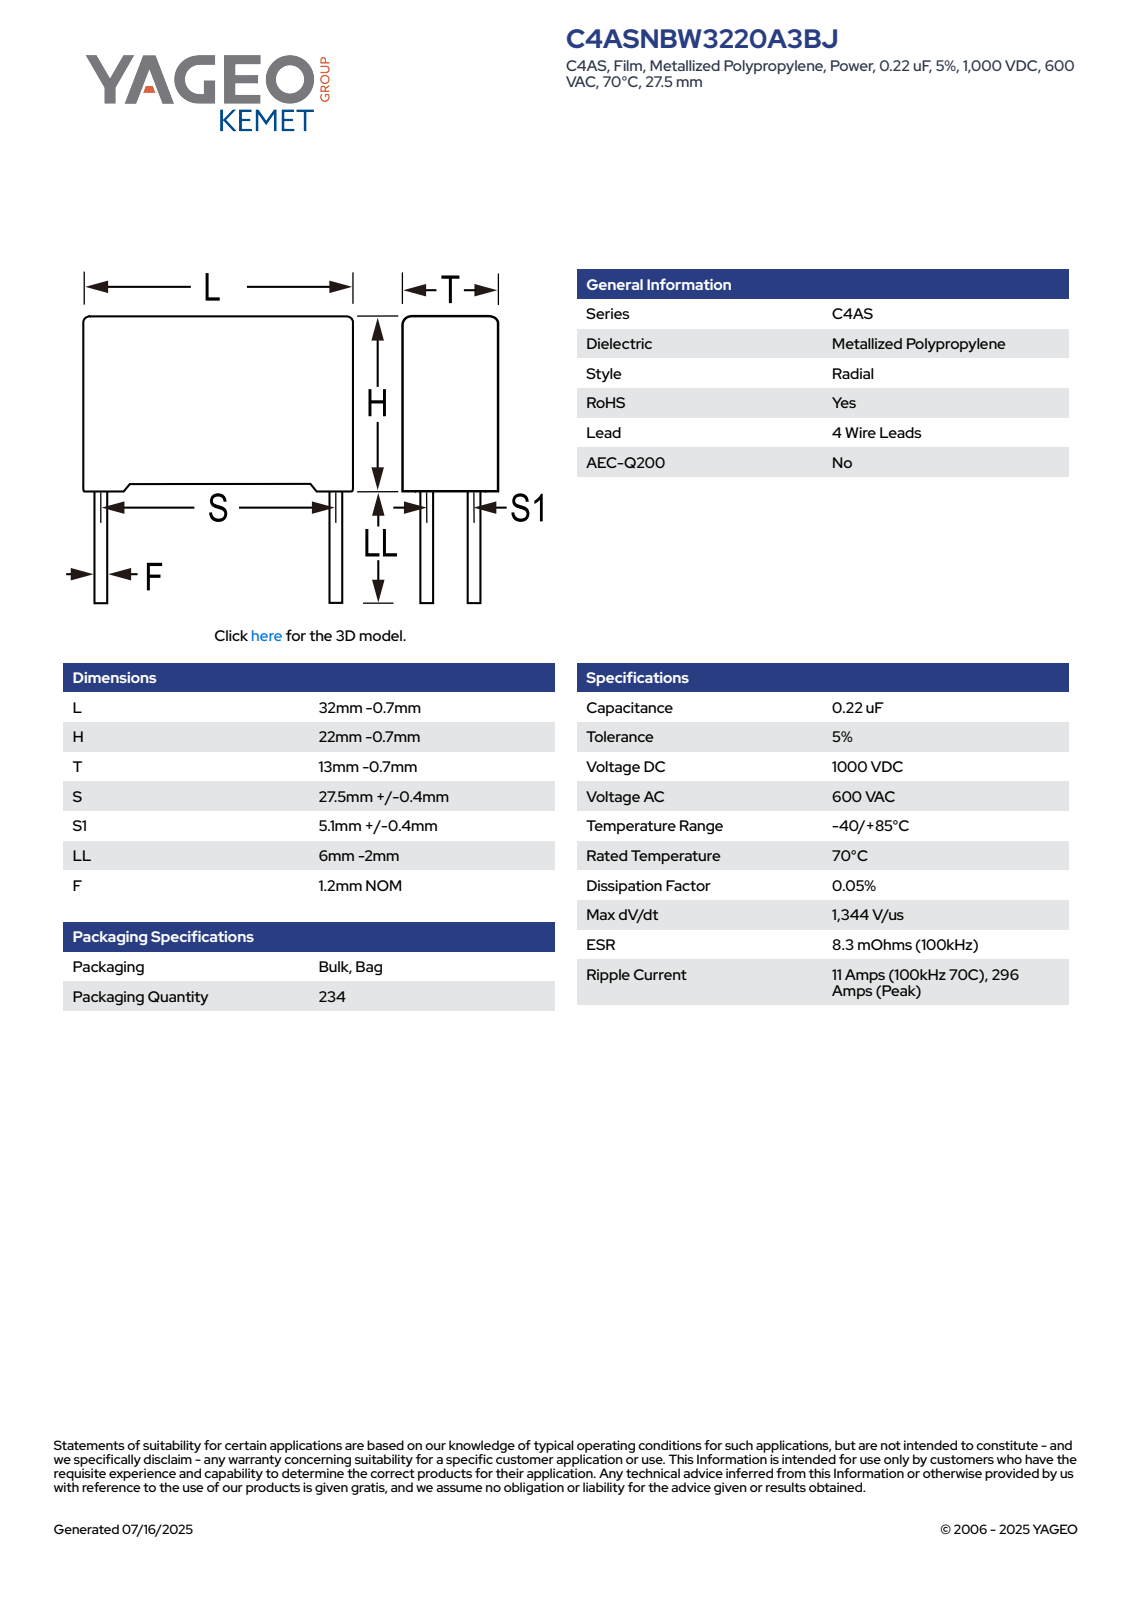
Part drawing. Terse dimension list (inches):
name: CFP_RB4_32X22X13_L31.3H21.3T12.3S27.5S15.1LL4F1.2
written by: SolidWorks 2014 (AUTOMOTIVE_DESIGN)
unit: in
bodies: 4 solids, 87 faces (79 planar, 8 cylindrical, 0 other)
size: 1.232 × 0.996 × 0.484
volume: 0.488 in³; area: 4.289 in²
bosses: 4× ⌀0.047
face distances: 0.484, 0.814, 1.232, 0.025, 0.839, 0.03, 0.454, 1.202, 0.424, 1.172
